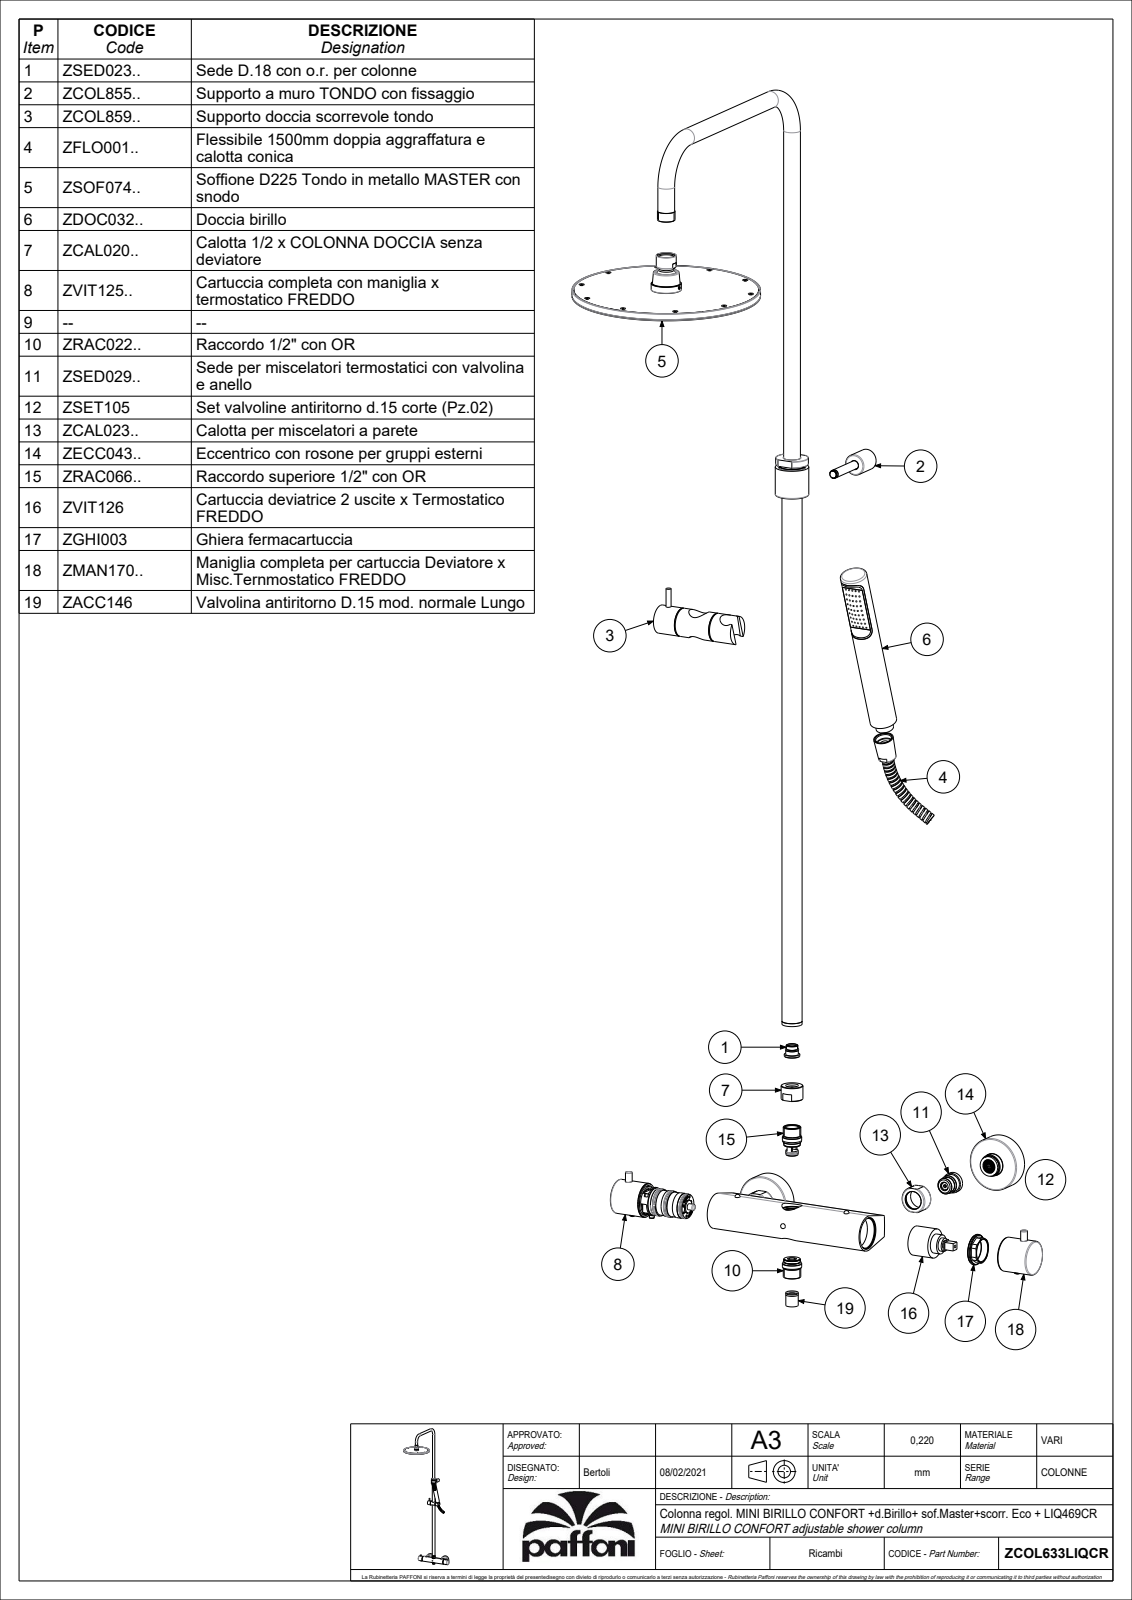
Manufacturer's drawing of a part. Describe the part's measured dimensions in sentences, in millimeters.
The part is named "ZCOL633LIQCR". Its 3-D file was written by "CREO PARAMETRIC BY PTC INC, 2020044 (CONFIG_CONTROL_DESIGN)". It is 11 solids with 3782 faces: 2069 planar, 815 cylindrical and 898 other. Overall it measures 1236 by 492.5 by 287.75 millimeters. Its volume is 880 578 cubic millimeters and its surface area 550 152 square millimeters. Round holes: 80 of diameter 1.2, 45 of diameter 1.5, 4 of diameter 4, 3 of diameter 10.5, 3 of diameter 15.1, 3 of diameter 16, 3 of diameter 17, 3 of diameter 24.5, 3 of diameter 25, 2 of diameter 2.5, 2 of diameter 3, 2 of diameter 3.25. Round bosses or shafts: 3 of diameter 40, 3 of diameter 24, 3 of diameter 20, 2 of diameter 63.5, 2 of diameter 41, 2 of diameter 27, 2 of diameter 23, 2 of diameter 21.2. Partial cylindrical surfaces (rounded edges, fillets, slot ends): 86 of radius 2.17, 30 of radius 1.68, 14 of radius 0.5, 8 of radius 1.18, 4 of radius 1.75, 2 of radius 1.2, 2 of radius 2.75, 2 of radius 2.96. The main face-to-face distances are 6.5, 0.6, 3.5, 3.49, 3.16, 51.5, 66.31, 65.71, 10, 3.45. The hole center spacings are 7.91, 13.76, 20.01, 6.5, 13, 26.39, 28.16, 90.
